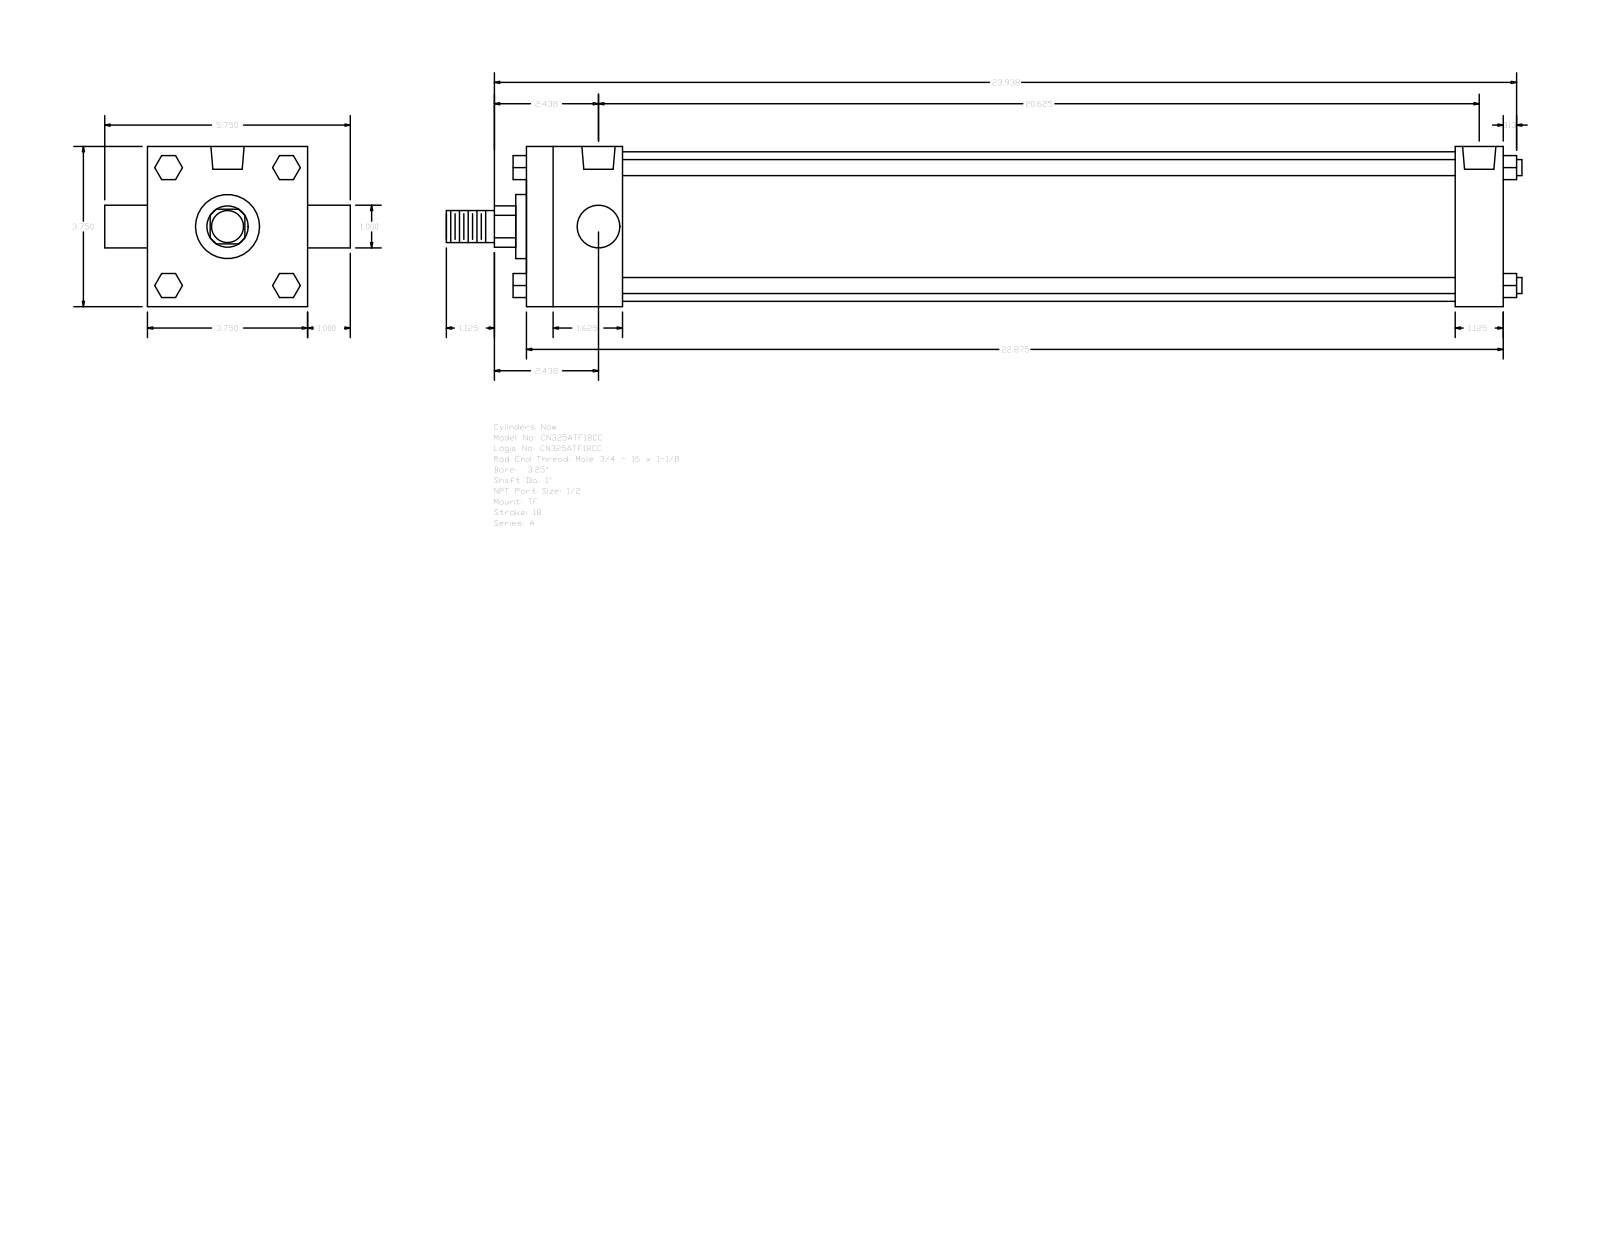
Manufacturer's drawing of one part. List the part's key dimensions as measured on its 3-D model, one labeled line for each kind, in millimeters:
Part name (STEP PRODUCT): A_TF__0325_1
STEP written by: GSSL Pune (CONFIG_CONTROL_DESIGN)
Units: millimetres
Bodies: 0 solids, 120 faces (92 planar, 28 cylindrical, 0 other)
Overall size (bounding box): 639.76 × 146.05 × 95.25
Round holes (diameter × count): ⌀8.73 ×3, ⌀19.77 ×2
Round bosses / shafts (diameter × count): ⌀9.53 ×4, ⌀25.4 ×2, ⌀88.9 ×1, ⌀38.1 ×1, ⌀19.05 ×1
Partial cylindrical surfaces — rounded edges, fillets, slot ends (radius × count): R12.29 ×1
Main face-to-face distances: 95.24, 581.03, 57.15, 552.45, 495.3, 523.88, 28.58, 14.28, 35.05, 60.71
Hole centre spacings: 3.18, 520.7, 517.52, 523.88
